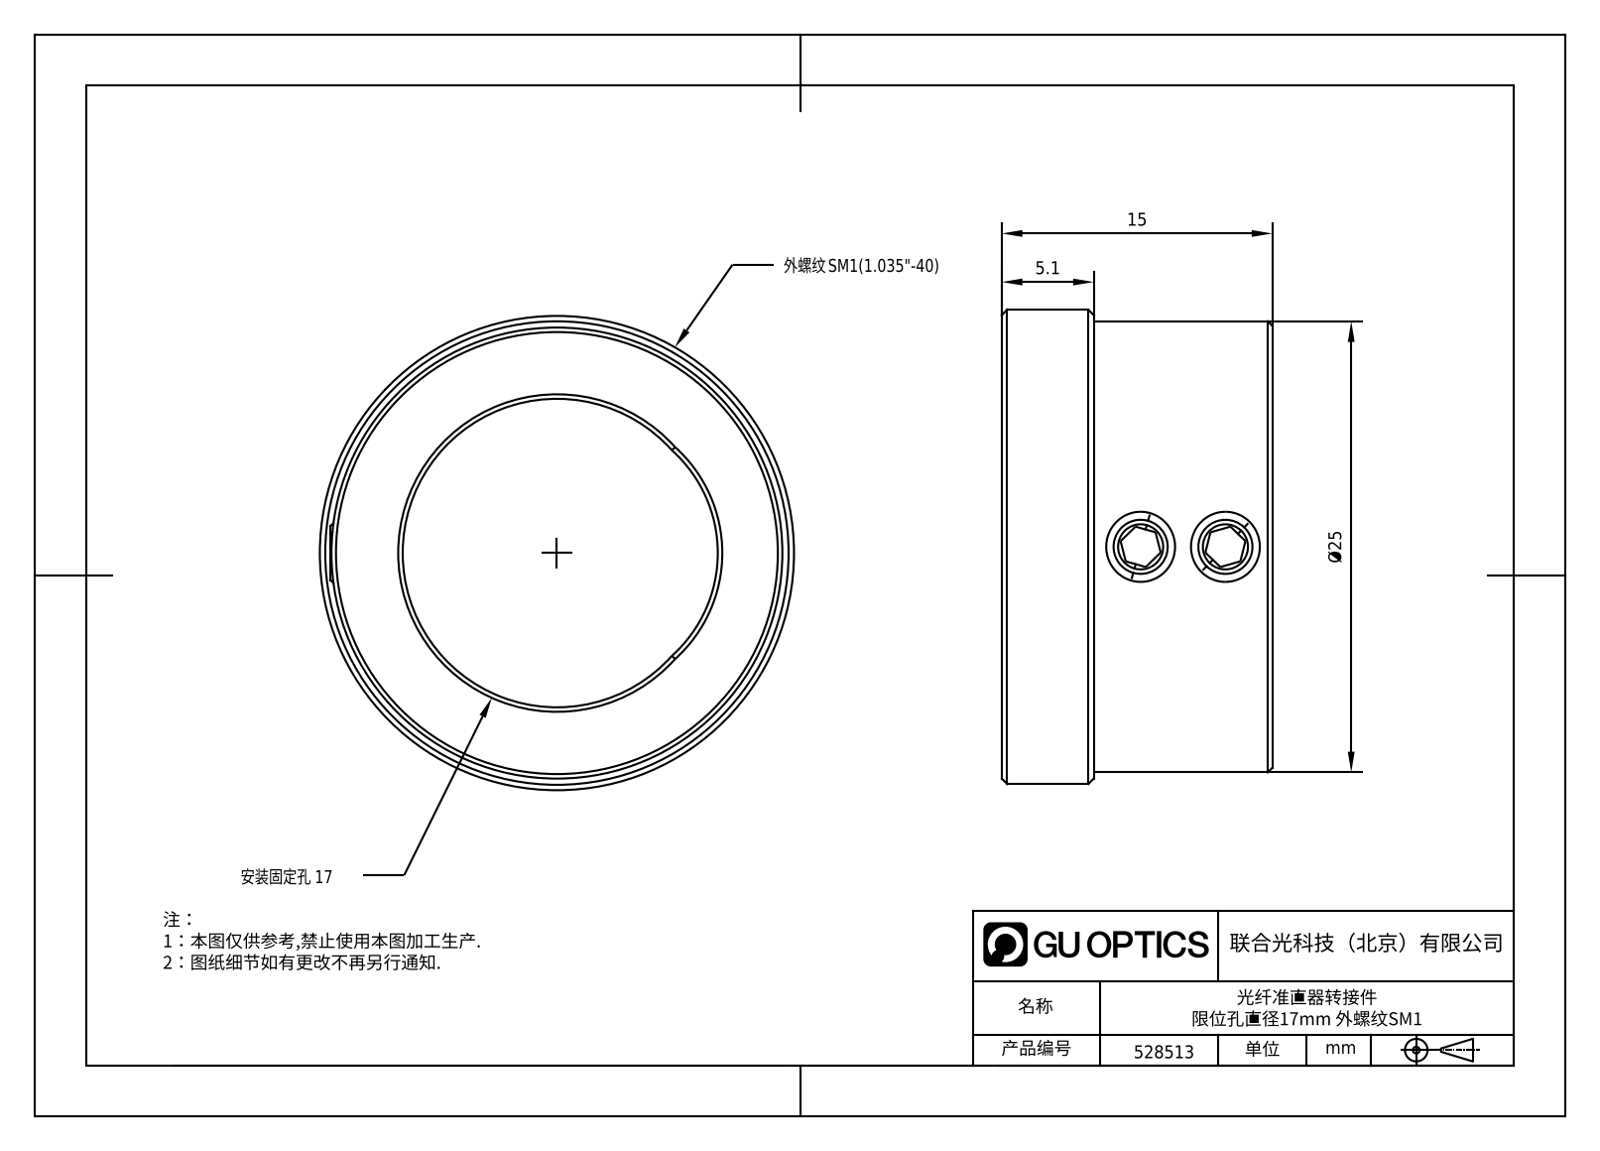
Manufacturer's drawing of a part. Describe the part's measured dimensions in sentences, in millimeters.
The part is named "30.8.8-14，M4尼龙头顶丝，A_30.8.56-LNJ4*3". Its 3-D file was written by "SolidWorks 2021 (CONFIG_CONTROL_DESIGN)". It is 3 solids with 77 faces: 23 planar, 24 cylindrical and 30 other. Overall it measures 26.29 by 26.29 by 15 millimeters. Its volume is 4 129 cubic millimeters and its surface area 2 770 square millimeters. Round holes: 2 of diameter 1.27, 2 of diameter 3.3. Round bosses or shafts: 2 of diameter 4, 2 of diameter 3, 1 of diameter 26.29, 1 of diameter 25. Partial cylindrical surfaces (rounded edges, fillets, slot ends): 1 of radius 7.65, 1 of radius 8.55. The main face-to-face distances are 15, 5.1, 9.9, 3, 2, 4, 1, 1.27, 3.83, 13.73. The hole center spacings are 4.7, 22.
